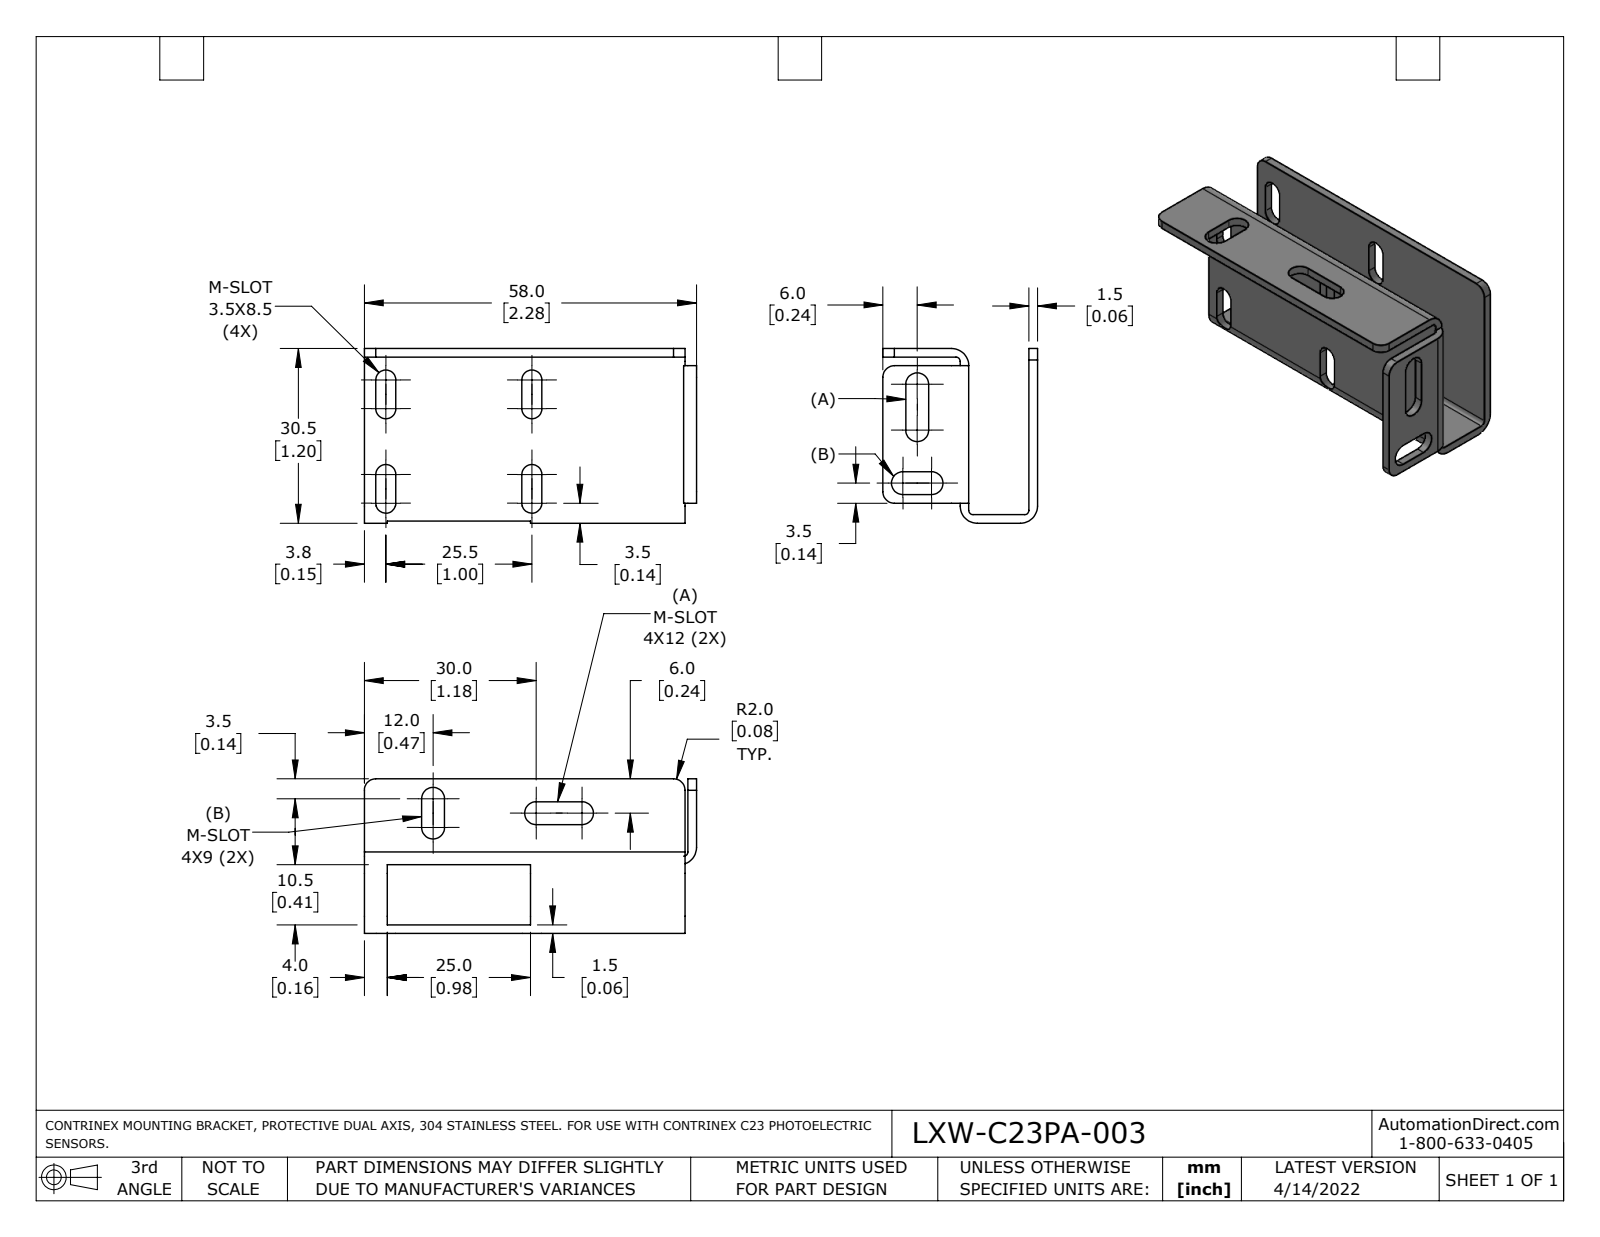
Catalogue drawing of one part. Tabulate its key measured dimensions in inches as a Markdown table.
| quantity | value |
| --- | --- |
| part name | LXW-C23PA-003 |
| STEP written by | PARTsolutions (AUTOMOTIVE_DESIGN) |
| units | inches |
| bodies | 1 solid, 88 faces (48 planar, 40 cylindrical, 0 other) |
| overall size | 2.283 × 1.201 × 1.063 |
| volume | 0.39 in³ |
| surface area | 14.92 in² |
| partial cylindrical surfaces (radius × count) | 0.079 × 14, 0.069 × 8, 0.03 × 4, 0.118 × 4 |
| main face-to-face distances | 0.059, 0.472, 0.531, 0.413, 1.142, 1.083, 1.201, 1.004, 1.063, 0.079 |
